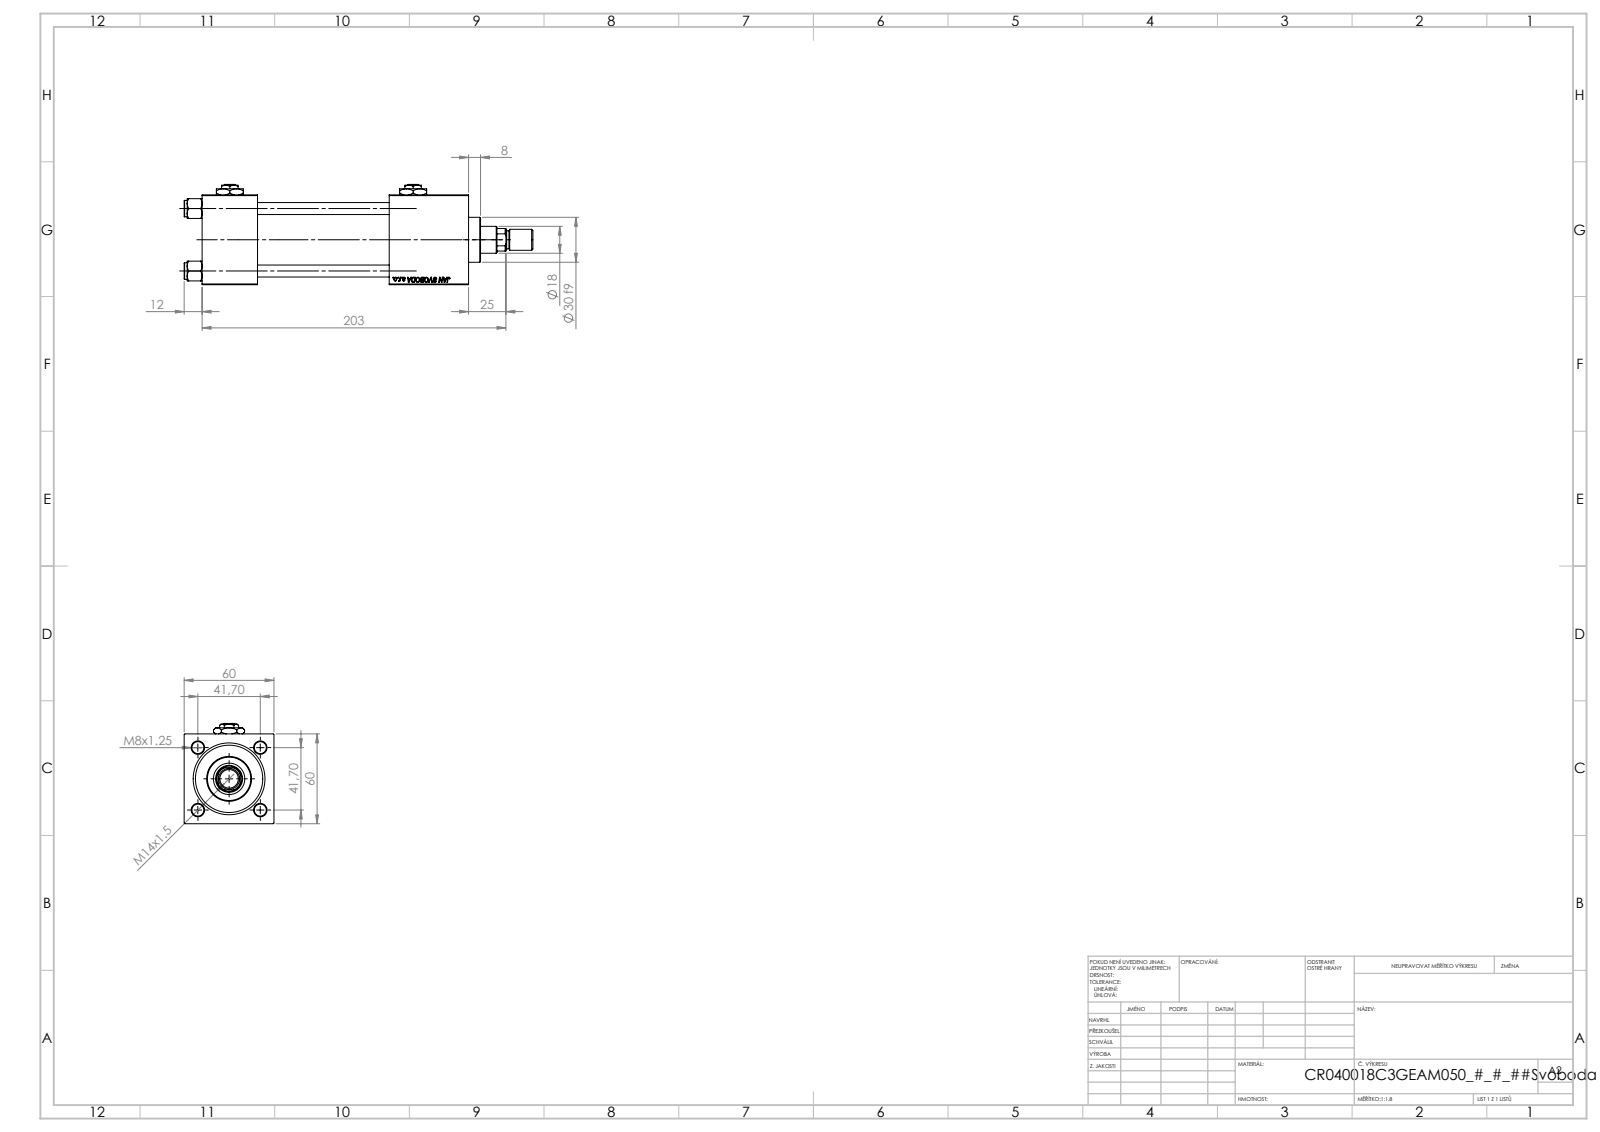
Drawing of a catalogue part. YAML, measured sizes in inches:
part_name: "V215CR_C_TYCINKA; V215_VC_A; V215CR_VCP_C; NUT_M5_C (+3 more)"
step_written_by: "SolidWorks 2019 (CONFIG_CONTROL_DESIGN)"
units: inches
bodies: {solids: 14, faces: 1264, planar: 578, cylindrical: 102, other: 584}
overall_size: [9.173, 2.638, 2.362]
volume: 26.08
surface_area: 189.5
round_holes:
  - {diameter: 0.315, count: 4}
  - {diameter: 0.276, count: 2}
  - {diameter: 0.656, count: 2}
  - {diameter: 0.945, count: 2}
  - {diameter: 0.335, count: 1}
  - {diameter: 0.709, count: 1}
  - {diameter: 0.827, count: 1}
  - {diameter: 1.22, count: 1}
  - {diameter: 1.575, count: 1}
  - {diameter: 1.772, count: 1}
round_bosses_or_shafts:
  - {diameter: 0.433, count: 4}
  - {diameter: 1.811, count: 1}
  - {diameter: 1.181, count: 1}
  - {diameter: 0.551, count: 1}
  - {diameter: 0.472, count: 1}
partial_cylinders:
  - {radius: 0.335, count: 1}
face_to_face_distances: [2.362, 1.457, 7.008, 5.551, 2.087, 4.921, 3.465, 5.878, 4.421, 0.957]
hole_center_spacings: [1.161, 1.642, 2.322, 4.823]
